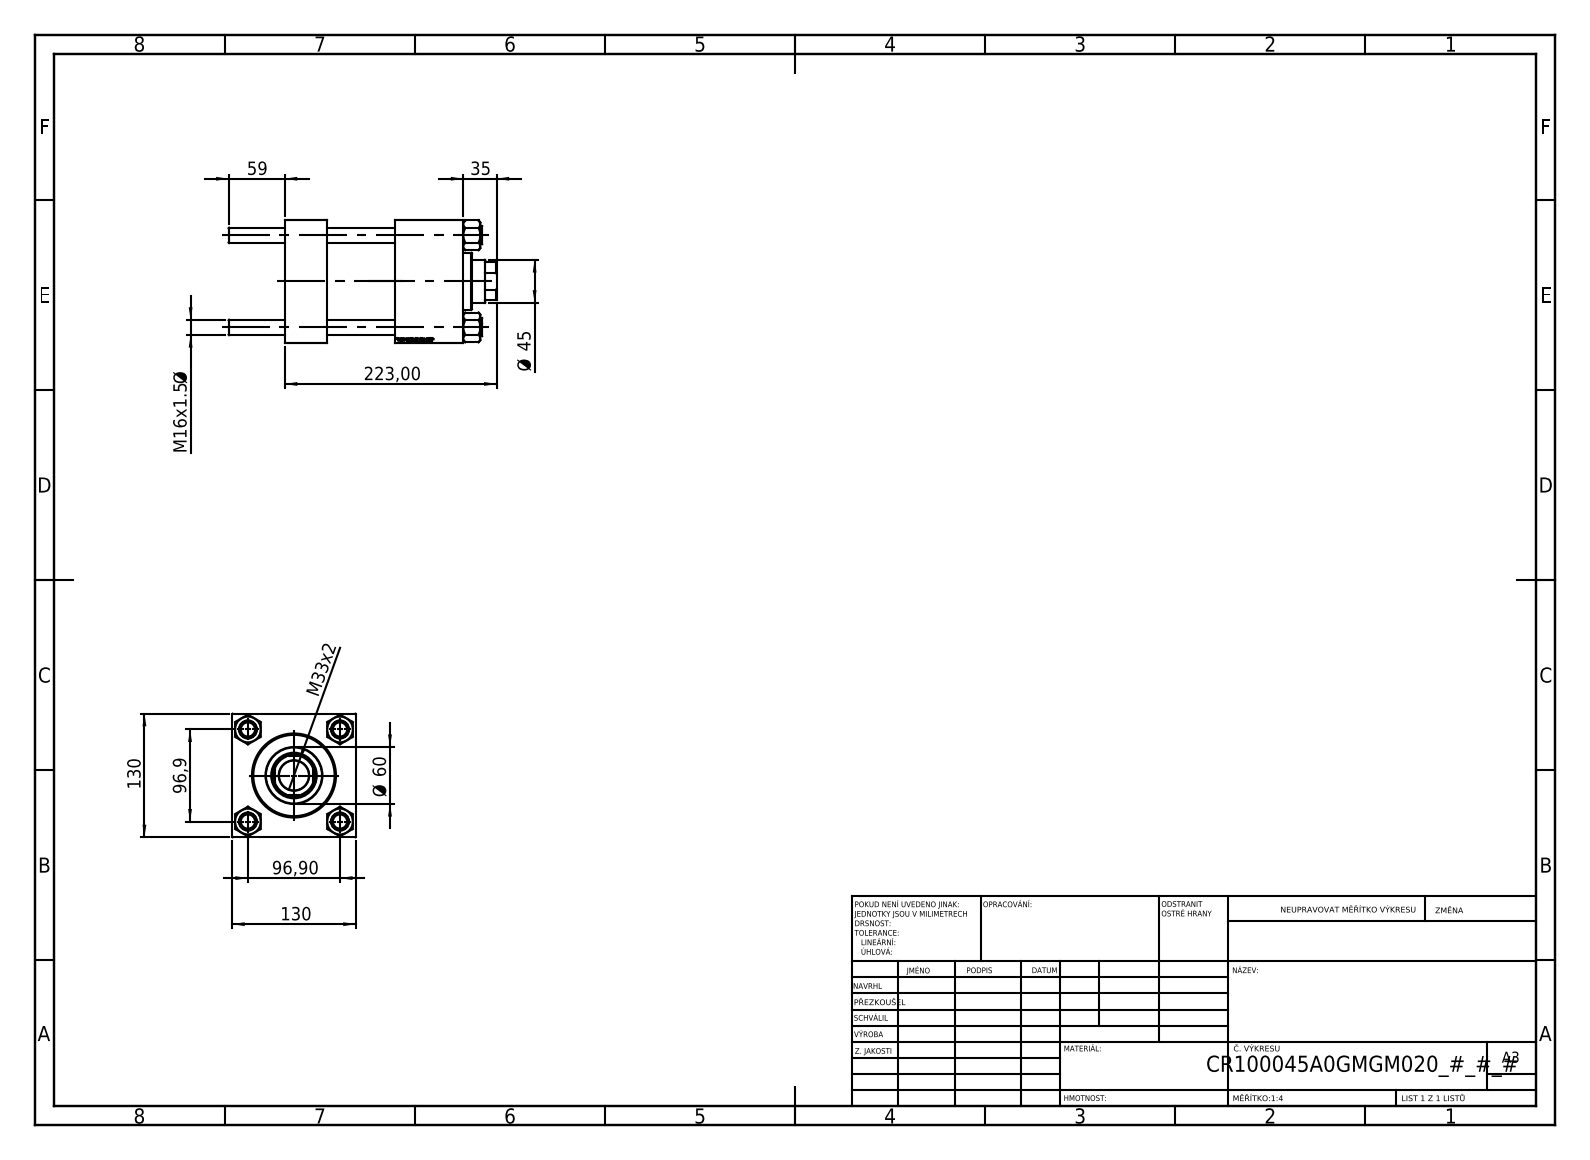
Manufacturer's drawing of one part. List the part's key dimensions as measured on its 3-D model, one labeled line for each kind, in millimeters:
Part name (STEP PRODUCT): V215_VC_A; V215CR_VCP; CR025_012_A_0_G_A_G_M_020_+#_##_TYCINKA; V215CR_BODY_A (+1 more)
STEP written by: SolidWorks 2019 (CONFIG_CONTROL_DESIGN)
Units: millimetres
Bodies: 11 solids, 1180 faces (566 planar, 78 cylindrical, 536 other)
Overall size (bounding box): 282 × 130 × 130
Volume: 2 497 000 mm³ · Surface area: 354 194 mm²
Round holes (diameter × count): ⌀16 ×4, ⌀7 ×2, ⌀26.44 ×2, ⌀35 ×2, ⌀31.5 ×1, ⌀45 ×1, ⌀48 ×1, ⌀76 ×1, ⌀85.5 ×1, ⌀100 ×1
Round bosses / shafts (diameter × count): ⌀19 ×4, ⌀106 ×1, ⌀60 ×1
Partial cylindrical surfaces — rounded edges, fillets, slot ends (radius × count): R22 ×1
Main face-to-face distances: 130, 45, 188, 143, 116, 71, 72, 20, 92, 96
Hole centre spacings: 68.52, 96.9, 137.04, 118.5
